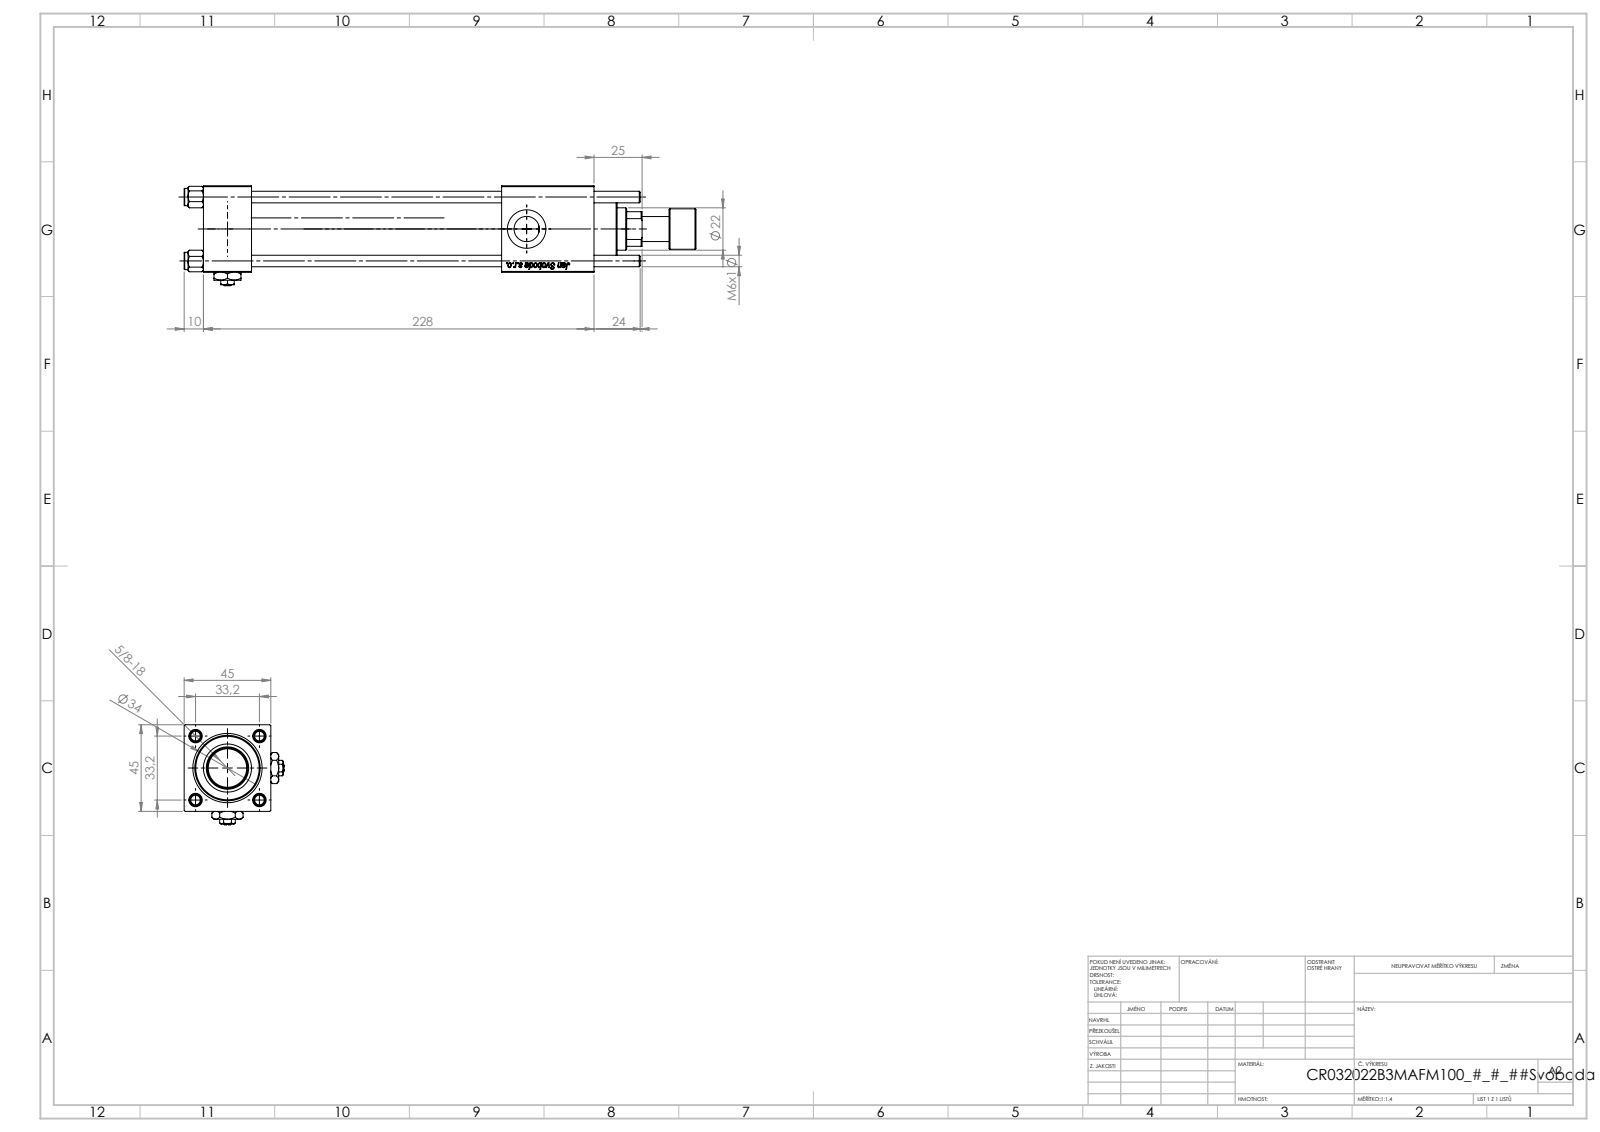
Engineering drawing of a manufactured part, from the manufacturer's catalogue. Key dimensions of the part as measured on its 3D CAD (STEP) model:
Part name (STEP PRODUCT): NUT_M5_B; V215CR_ROD_END_F; V215CR_B_TYCINKA; V215_VC_A (+3 more)
STEP written by: SolidWorks 2019 (CONFIG_CONTROL_DESIGN)
Units: millimetres
Bodies: 14 solids, 1267 faces (479 planar, 94 cylindrical, 694 other)
Overall size (bounding box): 266 × 52 × 52
Volume: 284 958 mm³ · Surface area: 110 001 mm²
Round holes (diameter × count): ⌀6 ×4, ⌀7 ×2, ⌀13.16 ×2, ⌀20 ×2, ⌀10.5 ×1, ⌀13 ×1, ⌀22 ×1, ⌀24 ×1, ⌀25 ×1, ⌀32 ×1, ⌀33 ×1
Round bosses / shafts (diameter × count): ⌀9 ×4, ⌀38 ×1, ⌀34 ×1, ⌀21 ×1, ⌀13 ×1
Main face-to-face distances: 45, 25, 203, 155, 130, 178, 48, 44.8, 174.3, 149.3
Hole centre spacings: 23.48, 33.2, 46.95
